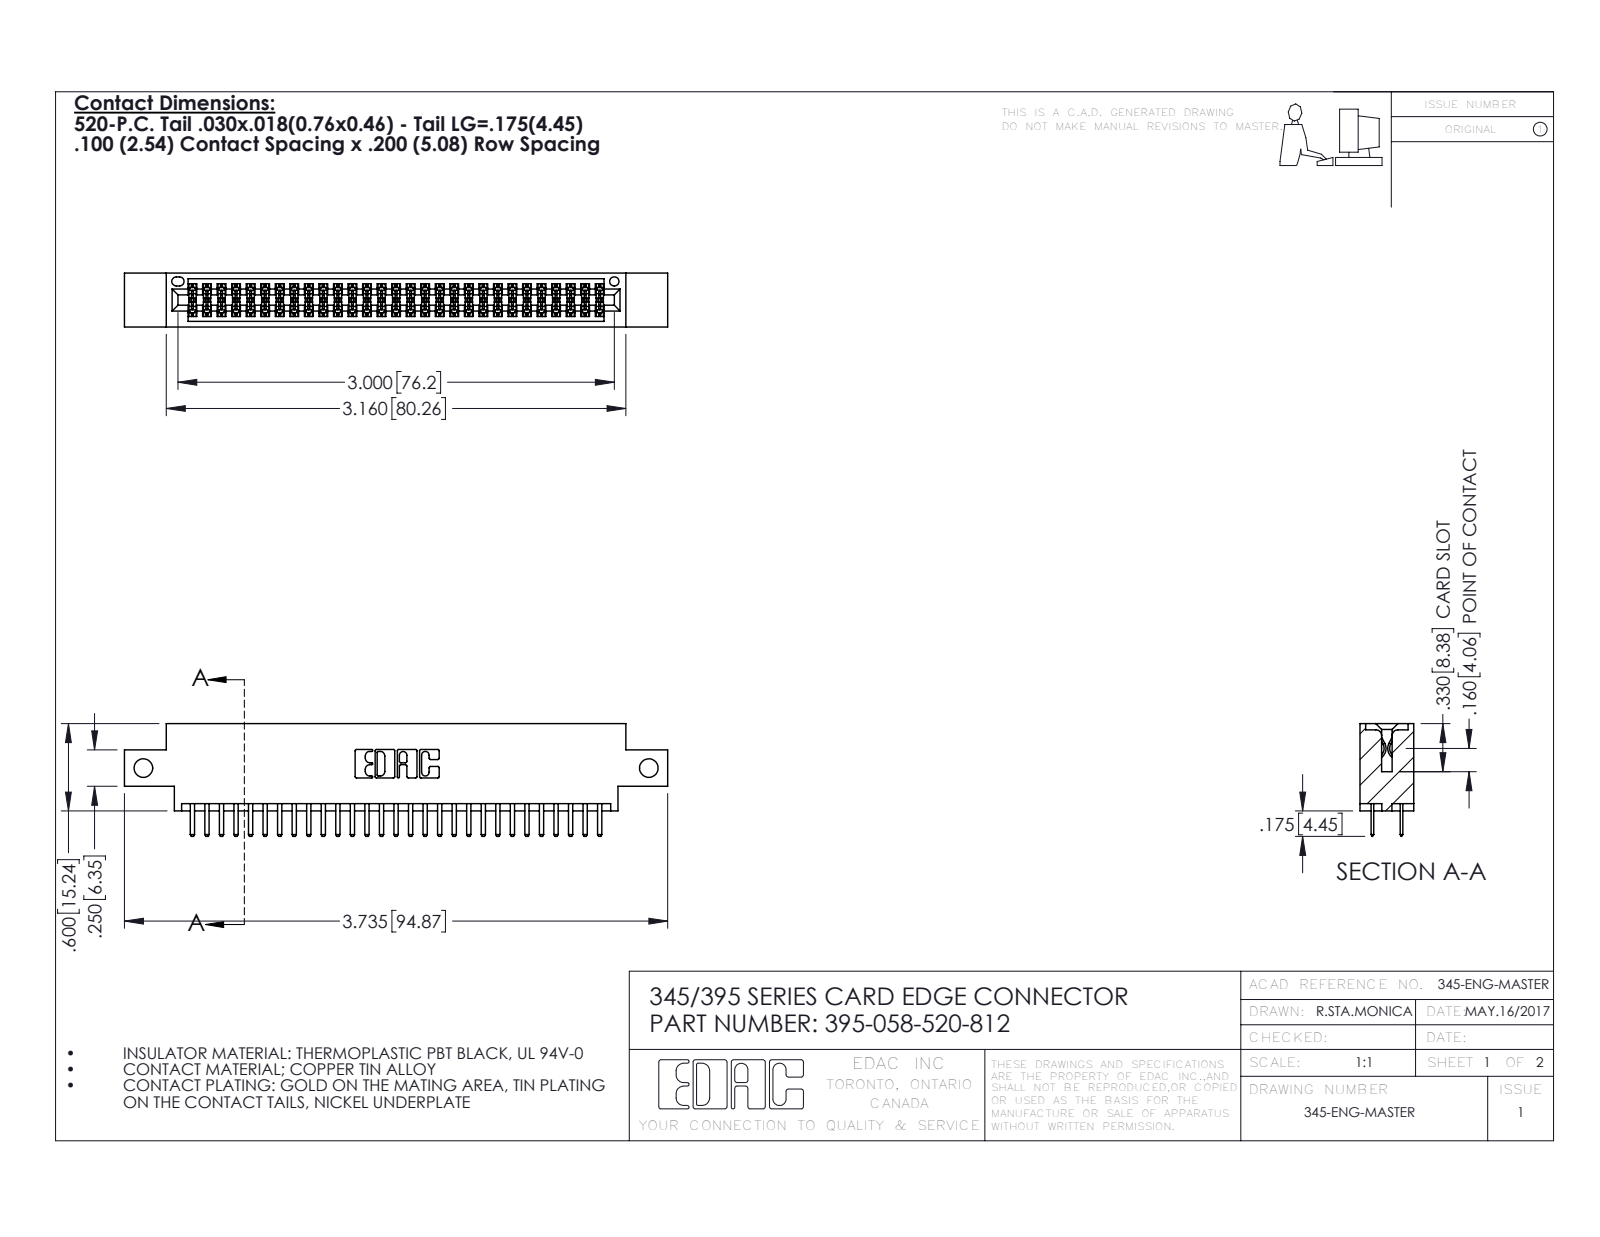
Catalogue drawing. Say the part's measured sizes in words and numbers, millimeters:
The part is named "345-292-001_345-293-120; 395-058-520-812; 345 Part_0.170 Offset - Side Mount". Its 3-D file was written by "SolidWorks 2016 (CONFIG_CONTROL_DESIGN)". It is 59 solids with 3262 faces: 2114 planar, 1148 cylindrical and 0 other. Overall it measures 94.9 by 19.7 by 9.4 millimeters. Its volume is 8 870 cubic millimeters and its surface area 12 810 square millimeters. Round holes: 2 of diameter 3.3, 1 of diameter 1.6. Partial cylindrical surfaces (rounded edges, fillets, slot ends): 87 of radius 0.2, 62 of radius 0.3, 22 of radius 0.3, 6 of radius 0.2, 6 of radius 0.8, 3 of radius 0.7, 2 of radius 0.4, 2 of radius 0.5. The main face-to-face distances are 7.6, 1.8, 5.1, 9.4, 2.5, 6.9, 0.6, 5.7, 0.6, 4.4. The hole center spacings are 88.3.
